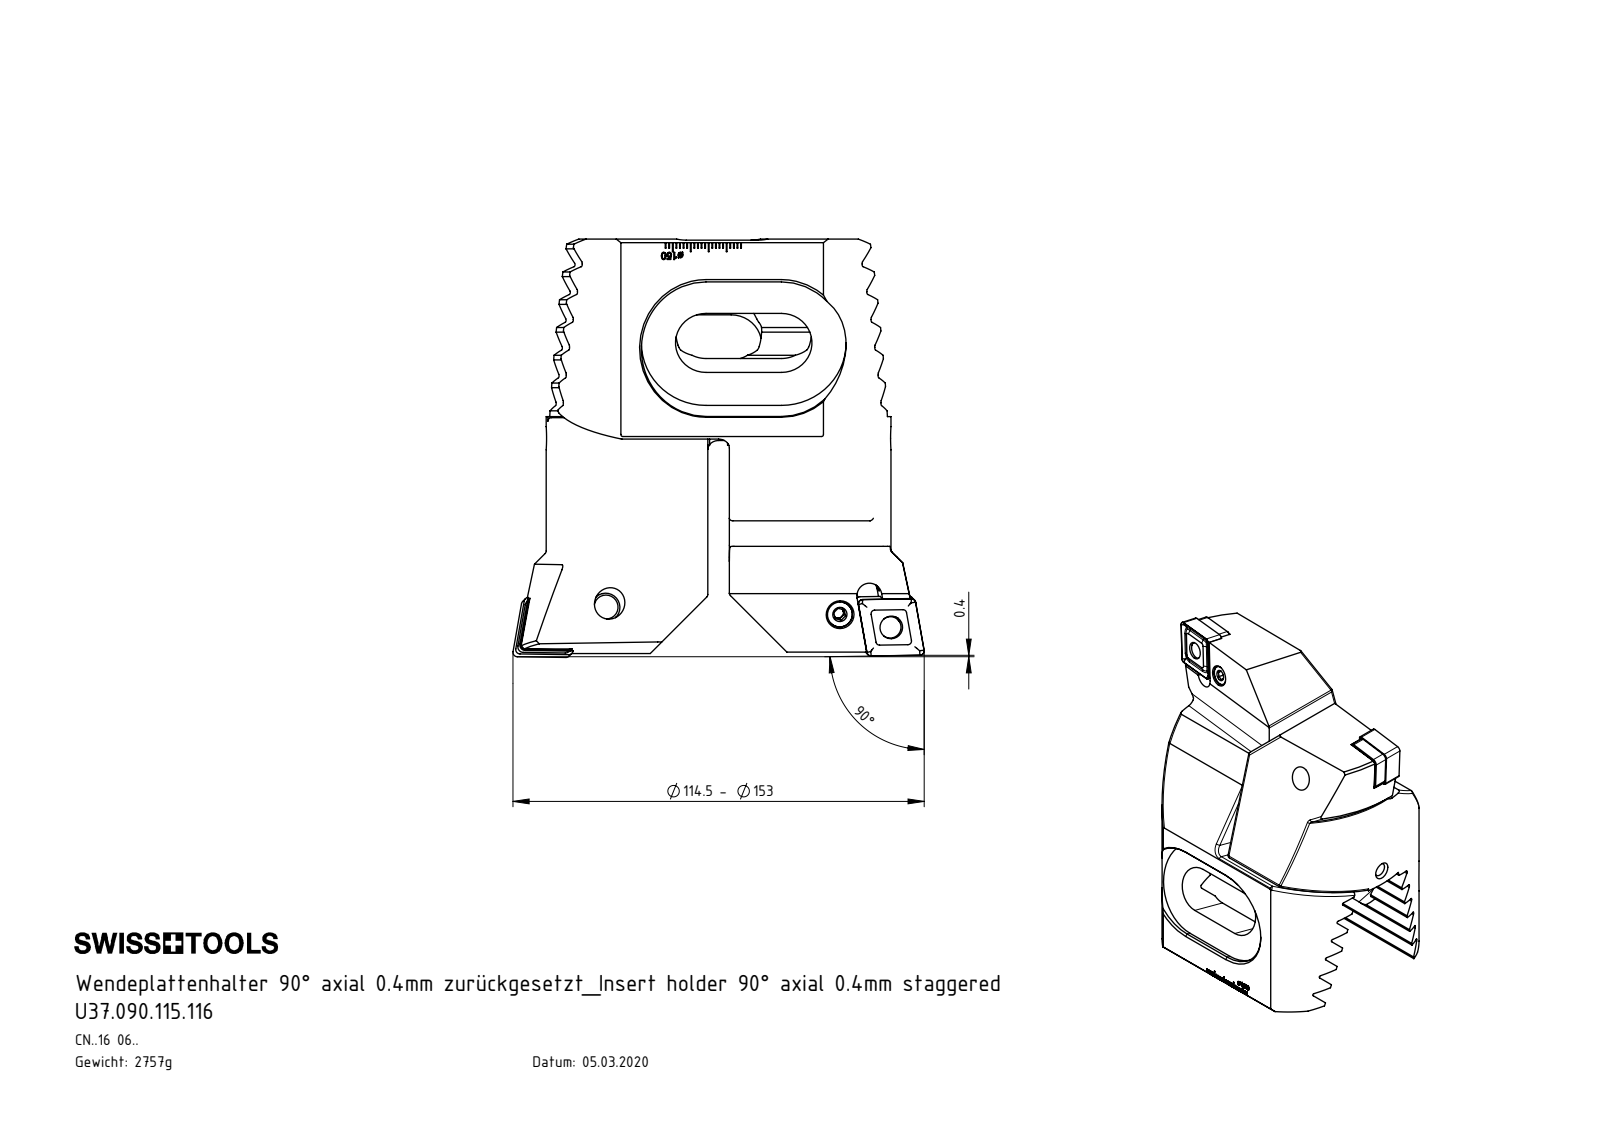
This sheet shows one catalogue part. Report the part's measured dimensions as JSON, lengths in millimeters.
{"part_name": "WCE-ER3.101.000_A; WCE-ER4.101.020_A; CNMG160612; WCE-ER2.101.004_A (+6 more)", "step_written_by": "SolidWorks 2017 (AUTOMOTIVE_DESIGN)", "units": "millimeters", "bodies": {"solids": 14, "faces": 879, "planar": 537, "cylindrical": 134, "other": 208}, "overall_size": [116.42, 114.5, 75.2], "volume_mm3": 351680, "surface_area_mm2": 70519, "round_holes": [[2, 4], [6.35, 2], [7, 2], [8.05, 2], [8.4, 2], [5, 1]], "round_bosses_or_shafts": [[6, 3], [8, 2], [7.9, 2], [6.4, 2], [3.55, 2], [4, 1]], "partial_cylinders_radius": [[0.58, 18], [1, 16], [1.2, 8], [1.5, 8], [3, 6], [3.5, 6], [0.3, 4], [8.5, 4]], "face_to_face_distances": [6.93, 13.86, 27.71, 20.79, 20.78, 6, 13.85, 27.72, 34.64, 6.92], "hole_center_spacings": [4, 14.76, 15, 25, 8, 25.31, 26.25, 46.87]}
